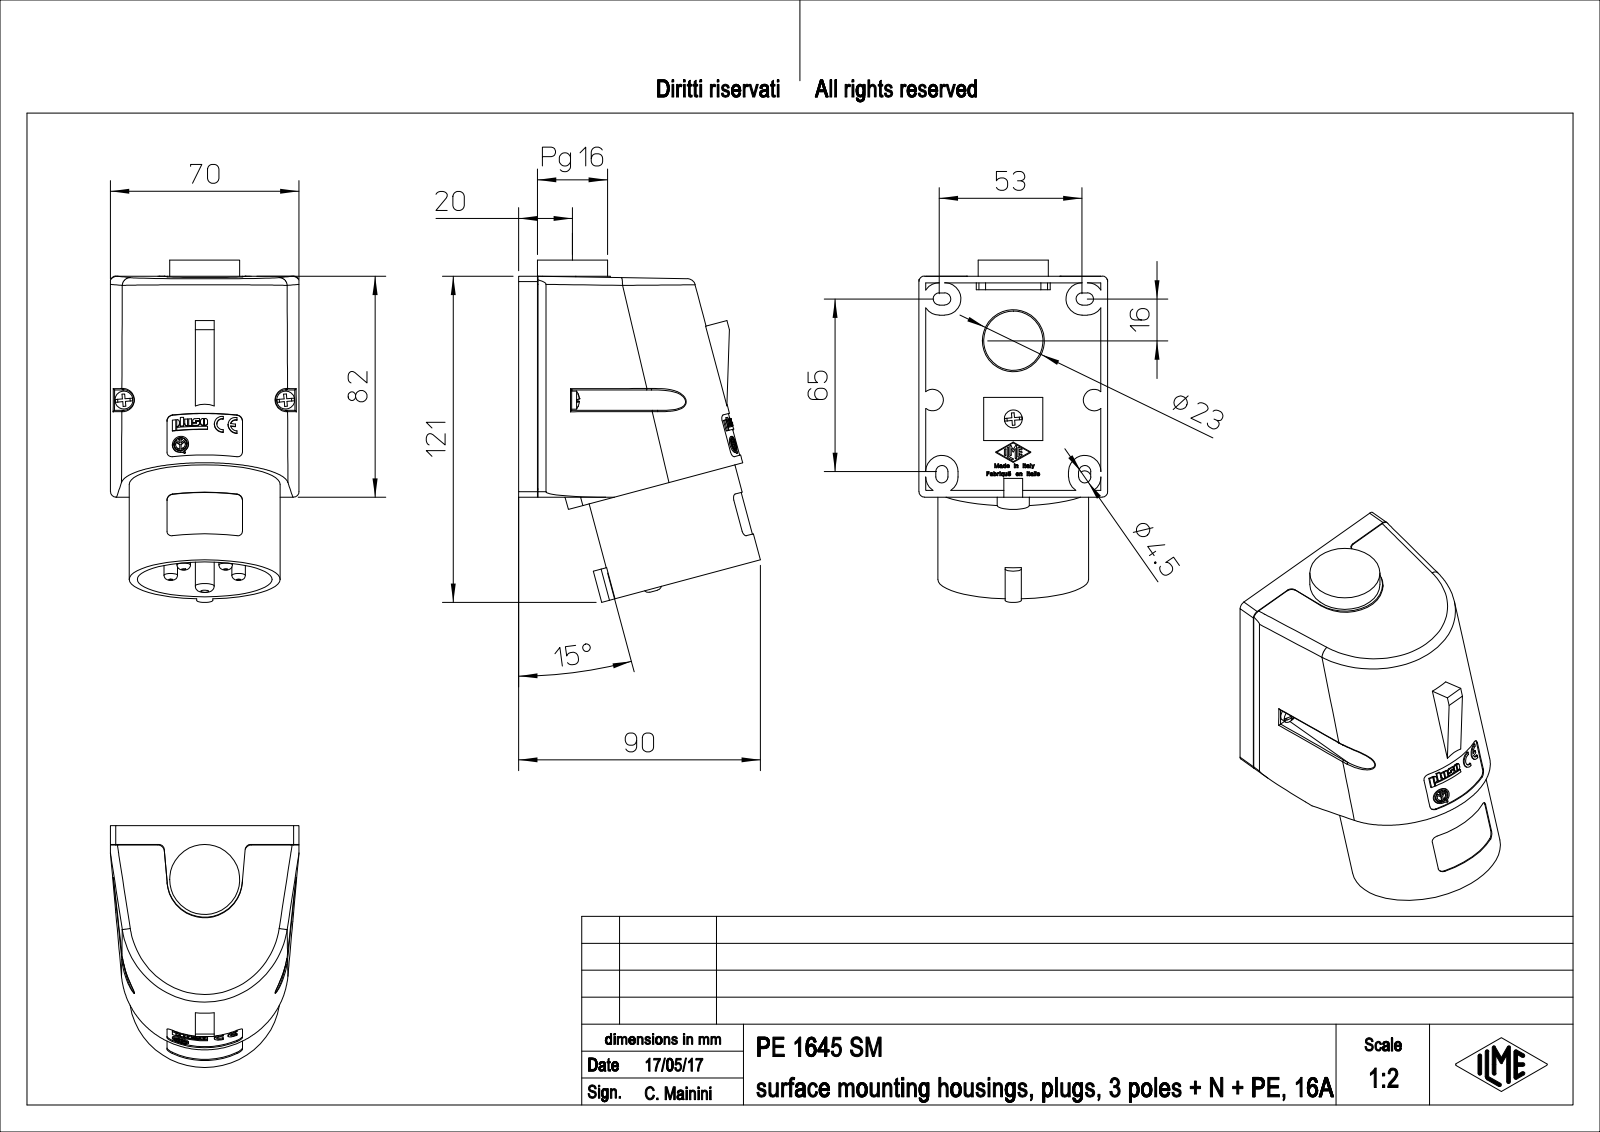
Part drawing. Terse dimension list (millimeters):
name: PE_1645_SM
written by: PTC Creo Elements/Direct Modeling 19.0E 27-Jun-2016 (C) Parametric Technology GmbH (AUTOMOTIVE_DESIGN)
unit: mm
bodies: 1 solid, 1845 faces (1561 planar, 188 cylindrical, 96 other)
size: 127.04 × 89.75 × 70
volume: 341 934 mm³; area: 67 379 mm²
holes: 2× ⌀3.2, 2× ⌀4.3, 2× ⌀4.5, 1× ⌀3, 1× ⌀5.04, 1× ⌀21.3, 1× ⌀23, 1× ⌀24, 1× ⌀50
bosses: 6× ⌀5, 5× ⌀6.7, 2× ⌀26, 1× ⌀56, 1× ⌀49, 1× ⌀7, 1× ⌀6
rounds: 15× R0.25, 14× R2, 13× R6, 9× R0.5, 9× R0.86, 8× R2.25, 8× R4, 6× R1
face distances: 2.5, 6.2, 3.7, 3.5, 6, 1, 7.2, 7, 82, 3
hole spacings: 37.2, 60
